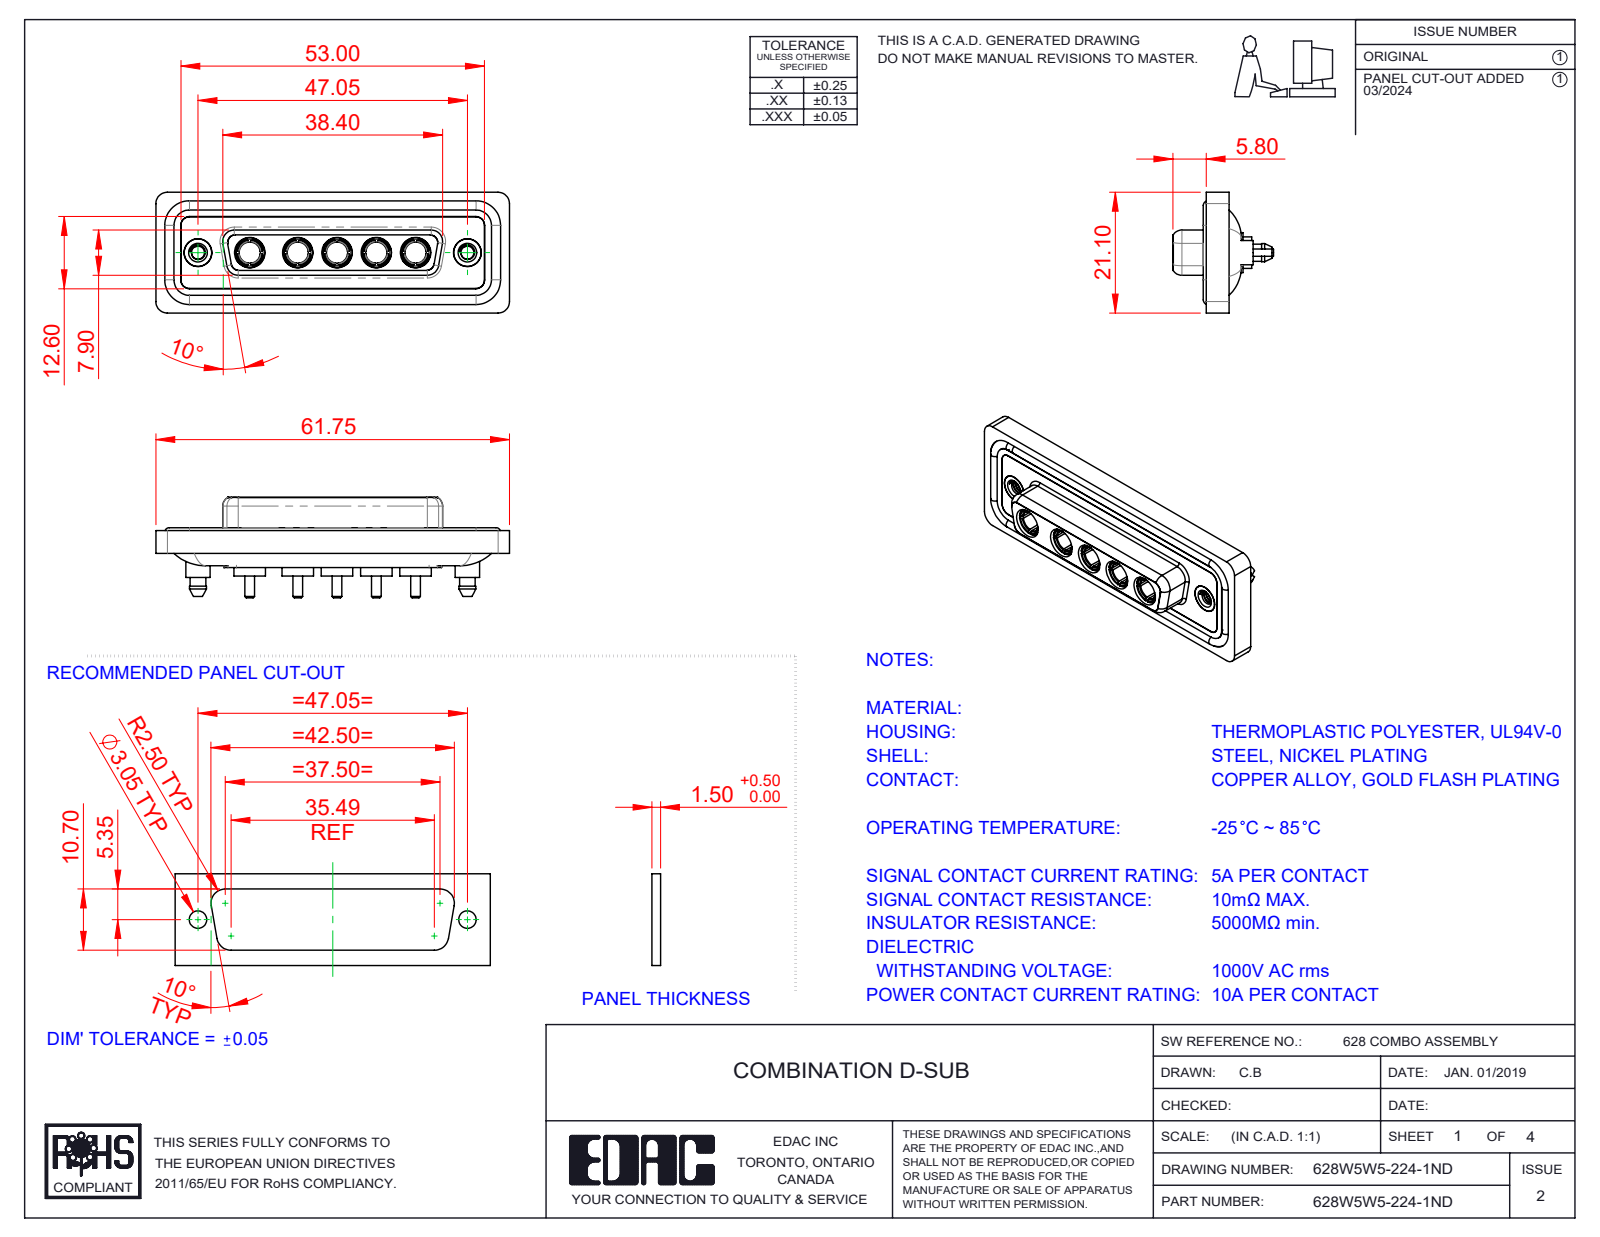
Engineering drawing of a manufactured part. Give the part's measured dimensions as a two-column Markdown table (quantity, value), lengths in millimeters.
| quantity | value |
| --- | --- |
| part name | 628Combo Waterproof Housing_25 Contacts; Power Socket_10A S; 628Combo Threaded Boardlock_D; 628Combo Housing_5W5 (+3 more) |
| STEP written by | SolidWorks 2023 (CONFIG_CONTROL_DESIGN) |
| units | millimeters |
| bodies | 17 solids, 822 faces (266 planar, 351 cylindrical, 205 other) |
| overall size | 61.75 × 21.1 × 17.55 |
| volume | 8 235 mm³ |
| surface area | 13 692 mm² |
| round holes (diameter × count) | 4.85 × 7, 3.7 × 5, 5.3 × 5, 2.26 × 2, 4 × 2, 4.05 × 2, 5 × 2 |
| round bosses / shafts (diameter × count) | 5.5 × 5, 5.2 × 5, 4.96 × 5, 4.75 × 5, 3.75 × 5, 1.7 × 5, 1.6 × 4, 5.4 × 2 |
| partial cylindrical surfaces (radius × count) | 1.5 × 24, 2 × 18, 1.6 × 10, 1.35 × 8, 2.1 × 5, 0.25 × 4, 0.5 × 4, 0.6 × 4 |
| main face-to-face distances | 0.4, 1.8, 7.45, 5.65, 0.5, 7.05, 6.6, 1.6, 1.1, 1.5 |
| hole center spacings | 6.86, 9.04, 13.72, 38.01, 8.39, 15.25, 15.9, 17.43 |
